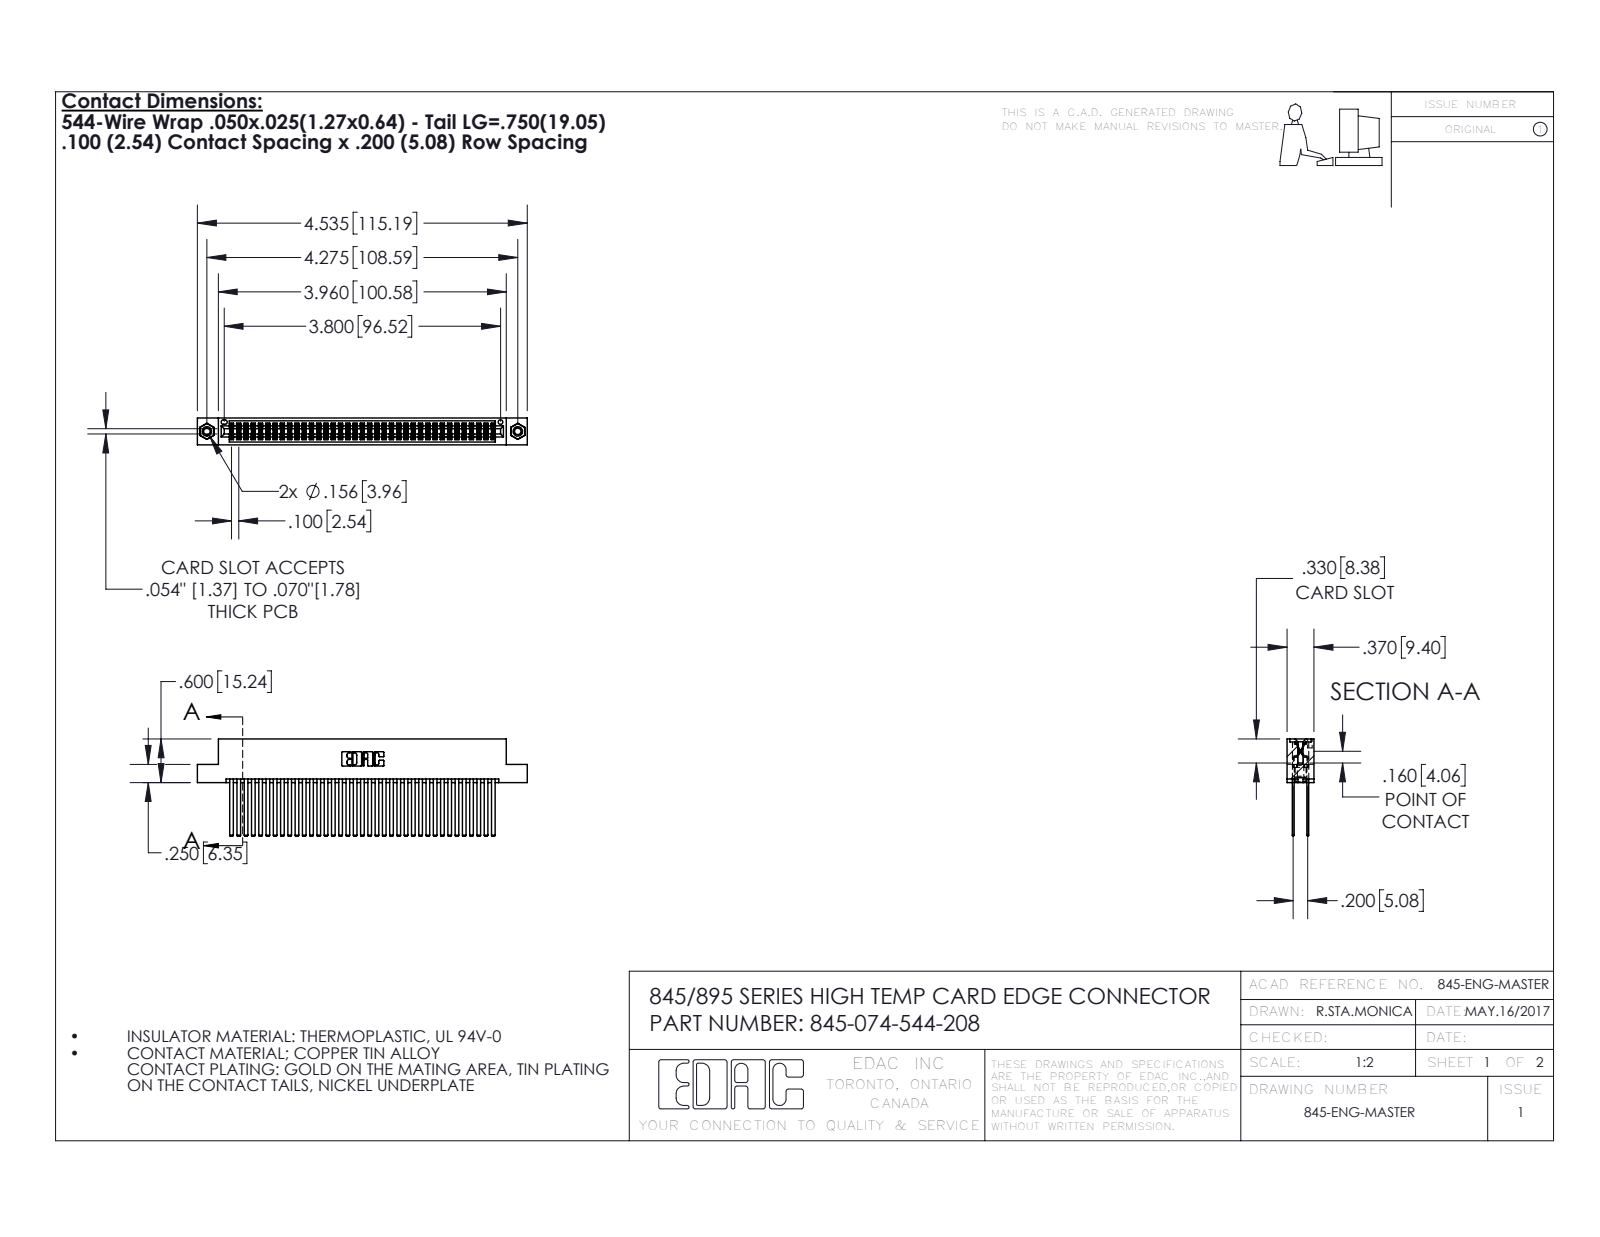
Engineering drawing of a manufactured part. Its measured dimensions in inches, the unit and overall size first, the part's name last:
Units: inches
Overall size (bounding box): 4.535 × 1.337 × 0.37
Round holes (diameter × count): ⌀0.089 ×2, ⌀0.125 ×2, ⌀0.156 ×2, ⌀0.064 ×1
Round bosses / shafts (diameter × count): ⌀0.155 ×2
Partial cylindrical surfaces — rounded edges, fillets, slot ends (radius × count): R0.006 ×111, R0.01 ×22, R0.007 ×6, R0.031 ×6, R0.026 ×3, R0.014 ×2, R0.019 ×2, R0.022 ×2
Main face-to-face distances: 0.2, 0.025, 0.072, 0.098, 0.272, 0.298, 0.225, 0.175, 0.37, 0.05
Hole centre spacings: 0.27, 4.039, 4.275
Volume: 0.743 in³ · Surface area: 32.48 in²
Bodies: 77 solids, 3442 faces (2258 planar, 1168 cylindrical, 16 other)
Part name (STEP PRODUCT): 345-074-544-208; 345-250-001_345-250-003-102; 345 Part_Flush Mounting Lugs - 0.156 Dia-TI; 345-292-001_345-293-144
STEP written by: SolidWorks 2016 (CONFIG_CONTROL_DESIGN)
